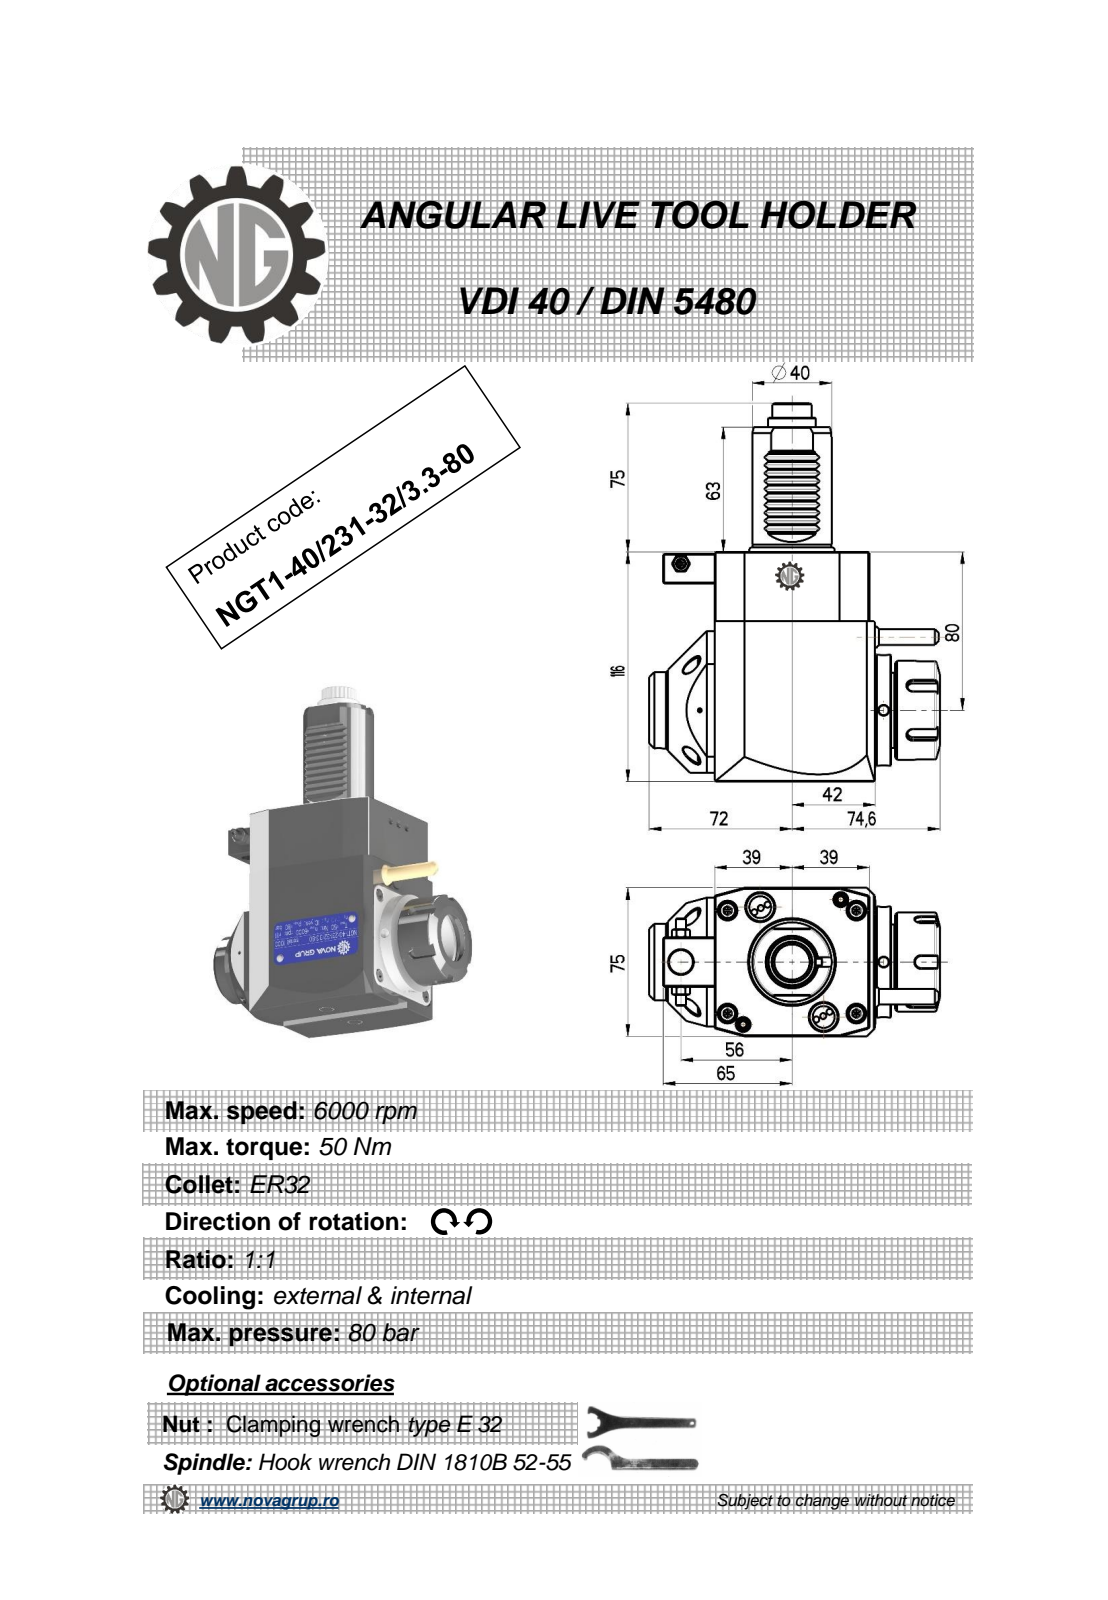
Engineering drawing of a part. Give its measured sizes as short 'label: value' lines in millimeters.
name: NGT1_40_231_32_3_3_80
written by: PRO/ENGINEER BY PARAMETRIC TECHNOLOGY CORPORATION, 2010280 (CONFIG_CONTROL_DESIGN)
unit: mm
bodies: 1 solid, 587 faces (229 planar, 193 cylindrical, 165 other)
size: 191 × 146.6 × 75
volume: 909 377 mm³; area: 73 357 mm²
holes: 3× ⌀5, 1× ⌀3, 1× ⌀4.2, 1× ⌀9.5, 1× ⌀12, 1× ⌀27
bosses: 1× ⌀56, 1× ⌀50, 1× ⌀43, 1× ⌀40, 1× ⌀38.5, 1× ⌀24, 1× ⌀11.2, 1× ⌀8.96
rounds: 48× R2.08, 20× R0.3, 12× R0.26, 6× R0.22, 5× R3, 1× R9.08, 1× R9.92, 1× R15
face distances: 75, 116, 81, 78, 3, 111, 7.5, 0.5, 80.8, 2.8
hole spacings: 38.68, 40.93, 71.5, 102.25, 126.22
